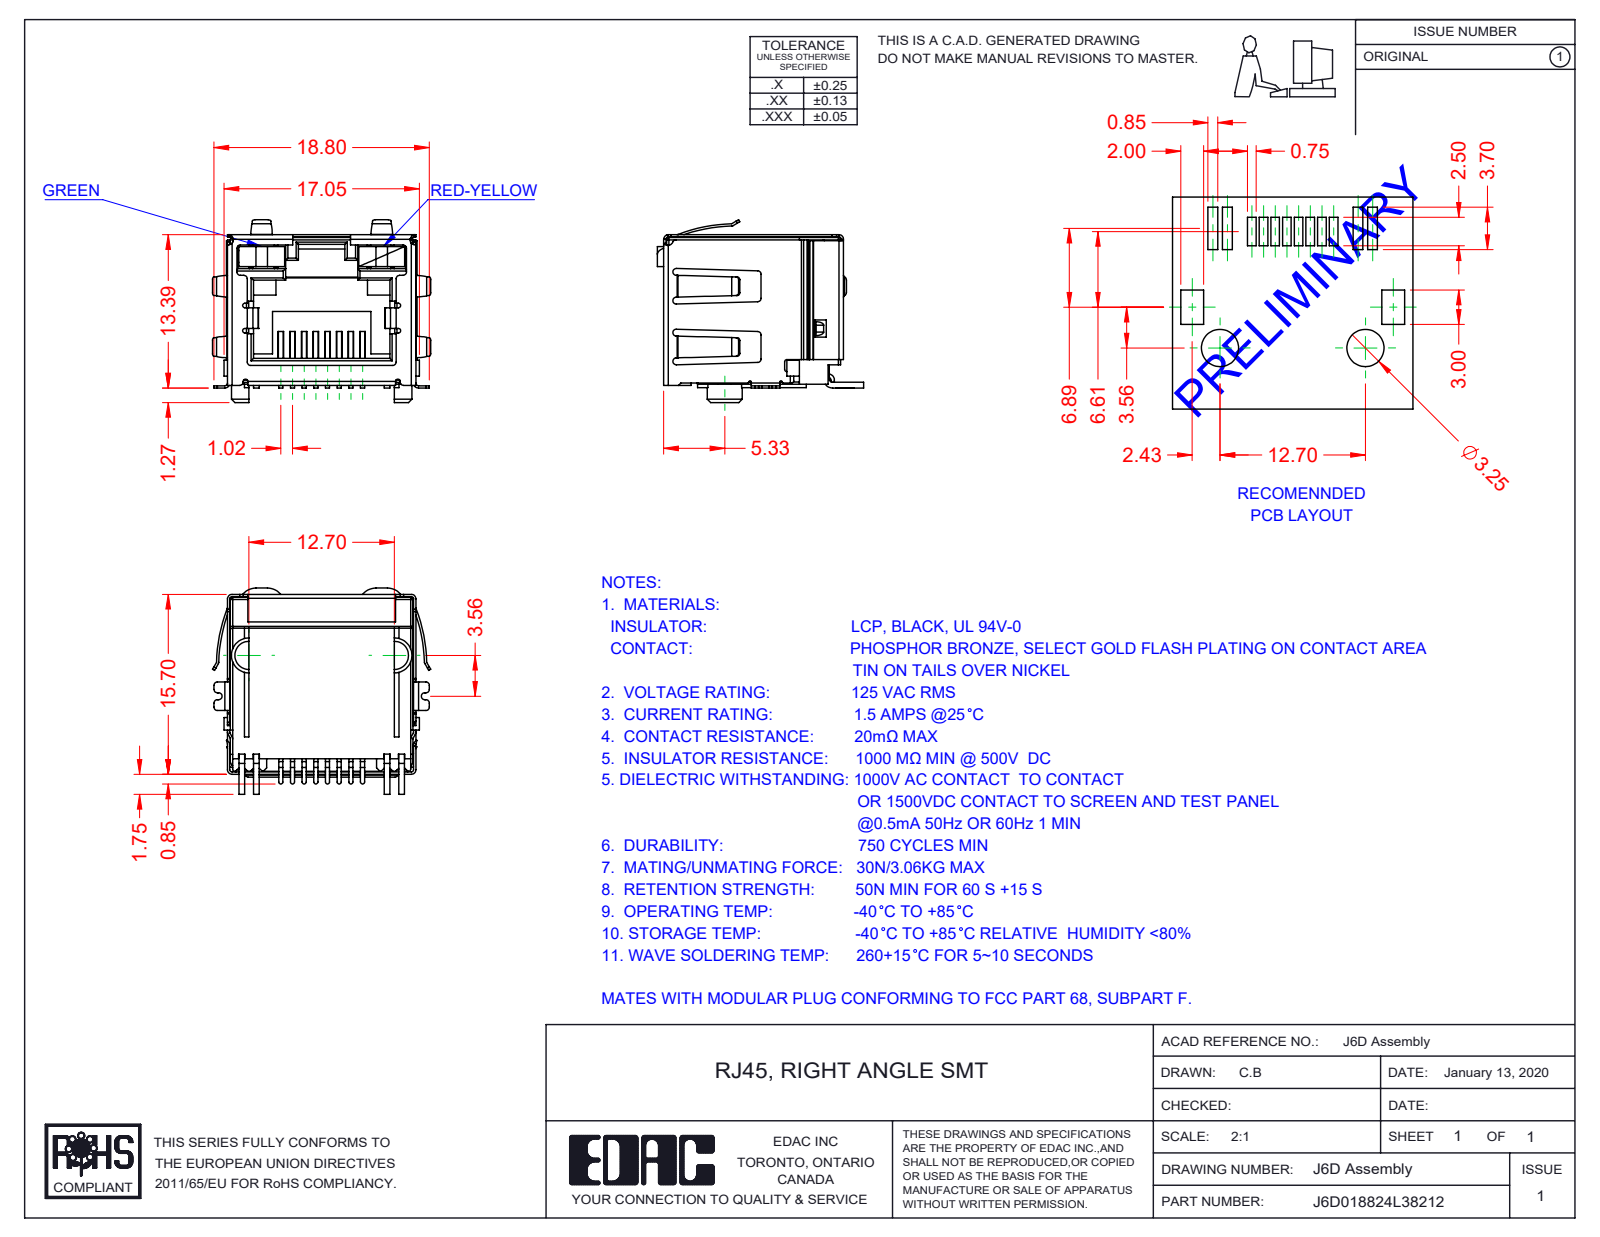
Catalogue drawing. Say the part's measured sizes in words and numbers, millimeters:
The part is named "6D Contacts; J6D018824L38212; 6D Shield_LED - EMI; 6D LED RH_8-Red-Yellow (+2 more)". Its 3-D file was written by "SolidWorks 2016 (CONFIG_CONTROL_DESIGN)". It is 12 solids with 1031 faces: 702 planar, 284 cylindrical and 45 other. Overall it measures 19.06 by 18 by 15.95 millimeters. Its volume is 1 790 cubic millimeters and its surface area 4 796 square millimeters. Partial cylindrical surfaces (rounded edges, fillets, slot ends): 55 of radius 0.3, 40 of radius 0.2, 19 of radius 0.4, 16 of radius 0.25, 12 of radius 0.1, 8 of radius 0.15, 8 of radius 0.18, 6 of radius 0.5. The main face-to-face distances are 16, 16.2, 16.25, 2.25, 1, 15.95, 12.8, 0.45, 13.05, 10.6.
